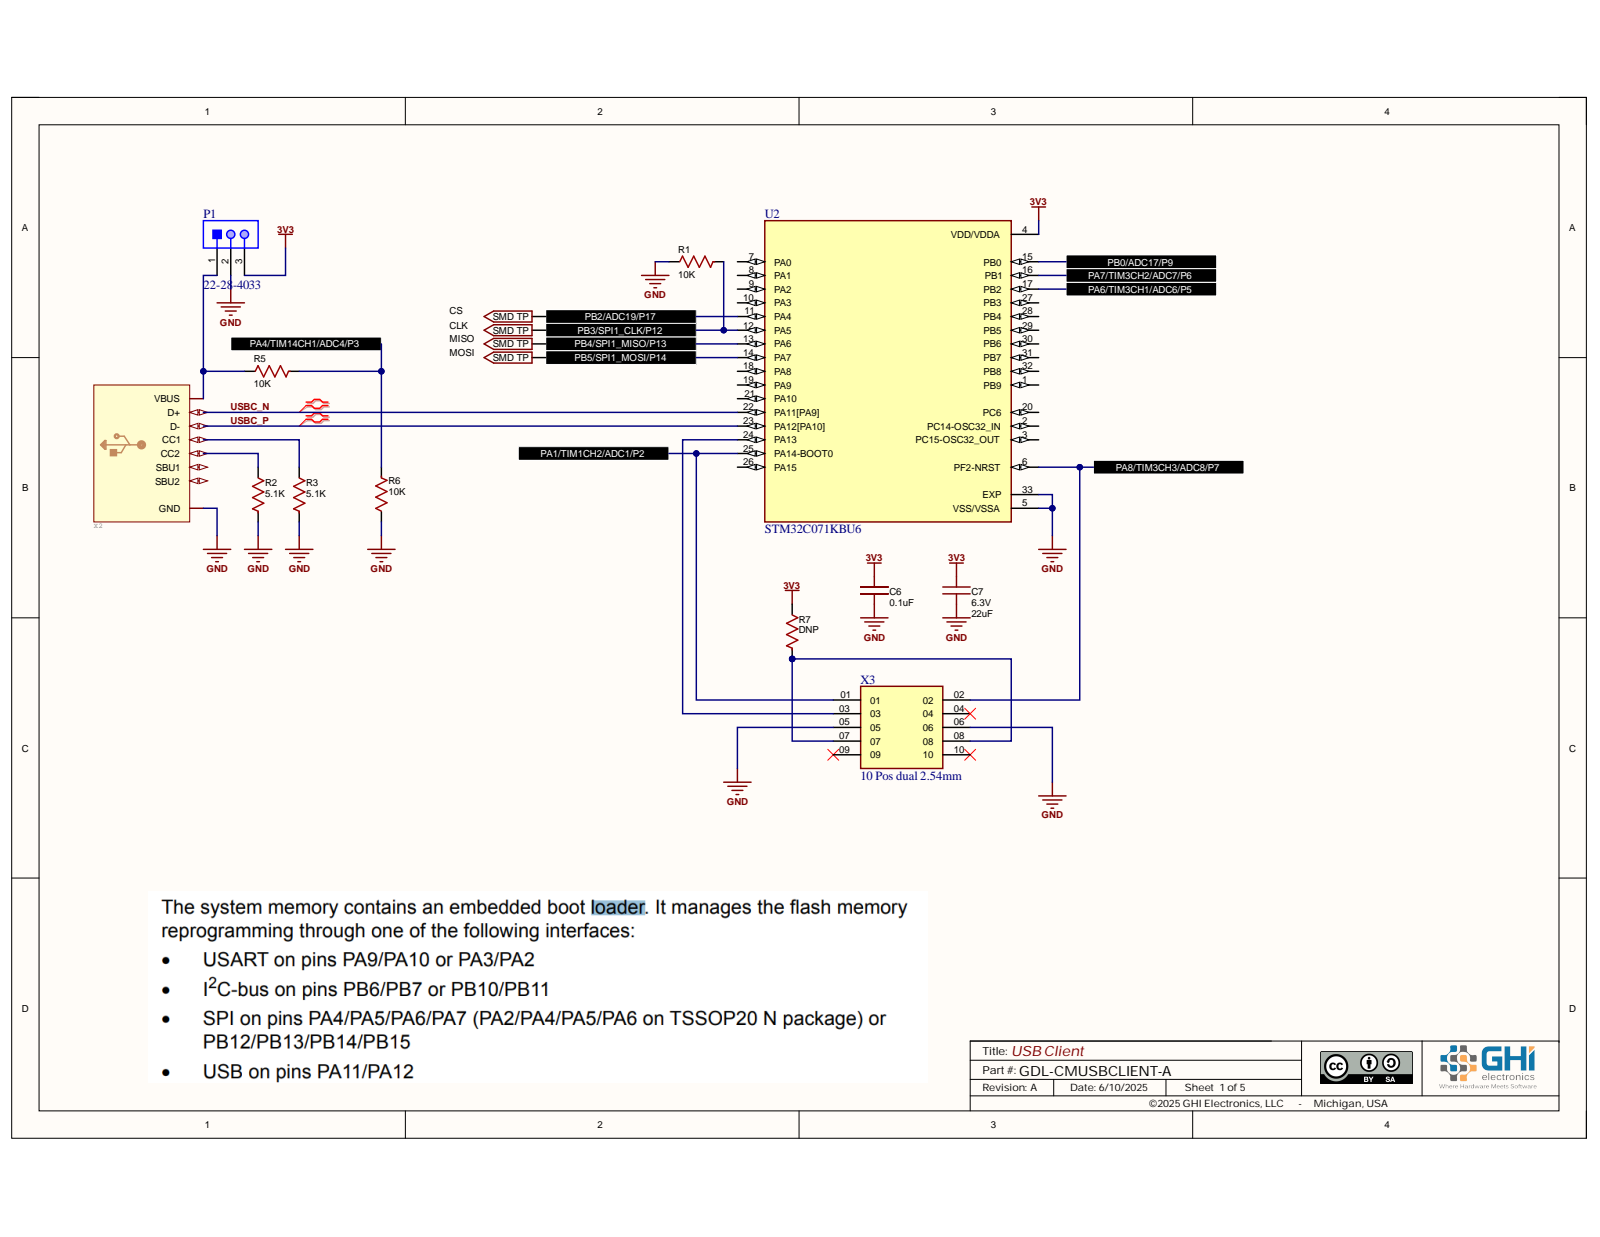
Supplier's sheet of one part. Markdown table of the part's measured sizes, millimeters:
| quantity | value |
| --- | --- |
| part name | PCB; Board; P1; 022284033 (+5 more) |
| STEP written by | Open CASCADE 7.5 (AUTOMOTIVE_DESIGN) |
| units | millimeters |
| bodies | 142 solids, 4492 faces (3187 planar, 923 cylindrical, 382 other) |
| overall size | 37 × 27 × 11.56 |
| volume | 477 mm³ |
| surface area | 3 501 mm² |
| round holes (diameter × count) | 3 × 4, 1.02 × 3, 1.42 × 3, 0.65 × 2, 1.02 × 2 |
| round bosses / shafts (diameter × count) | 0.5 × 2 |
| partial cylindrical surfaces (radius × count) | 0.15 × 98, 0.12 × 70, 0.2 × 53, 0.1 × 50, 0.4 × 16, 0.13 × 15, 0.17 × 15, 0.3 × 12 |
| main face-to-face distances | 0.45, 1.23, 0.35, 0.7, 0.93, 1.93, 1.28, 3.11, 1.63, 0.66 |
| hole center spacings | 2.54, 5.1, 12.45, 18.12, 20, 20.31, 20.44, 20.96 |
